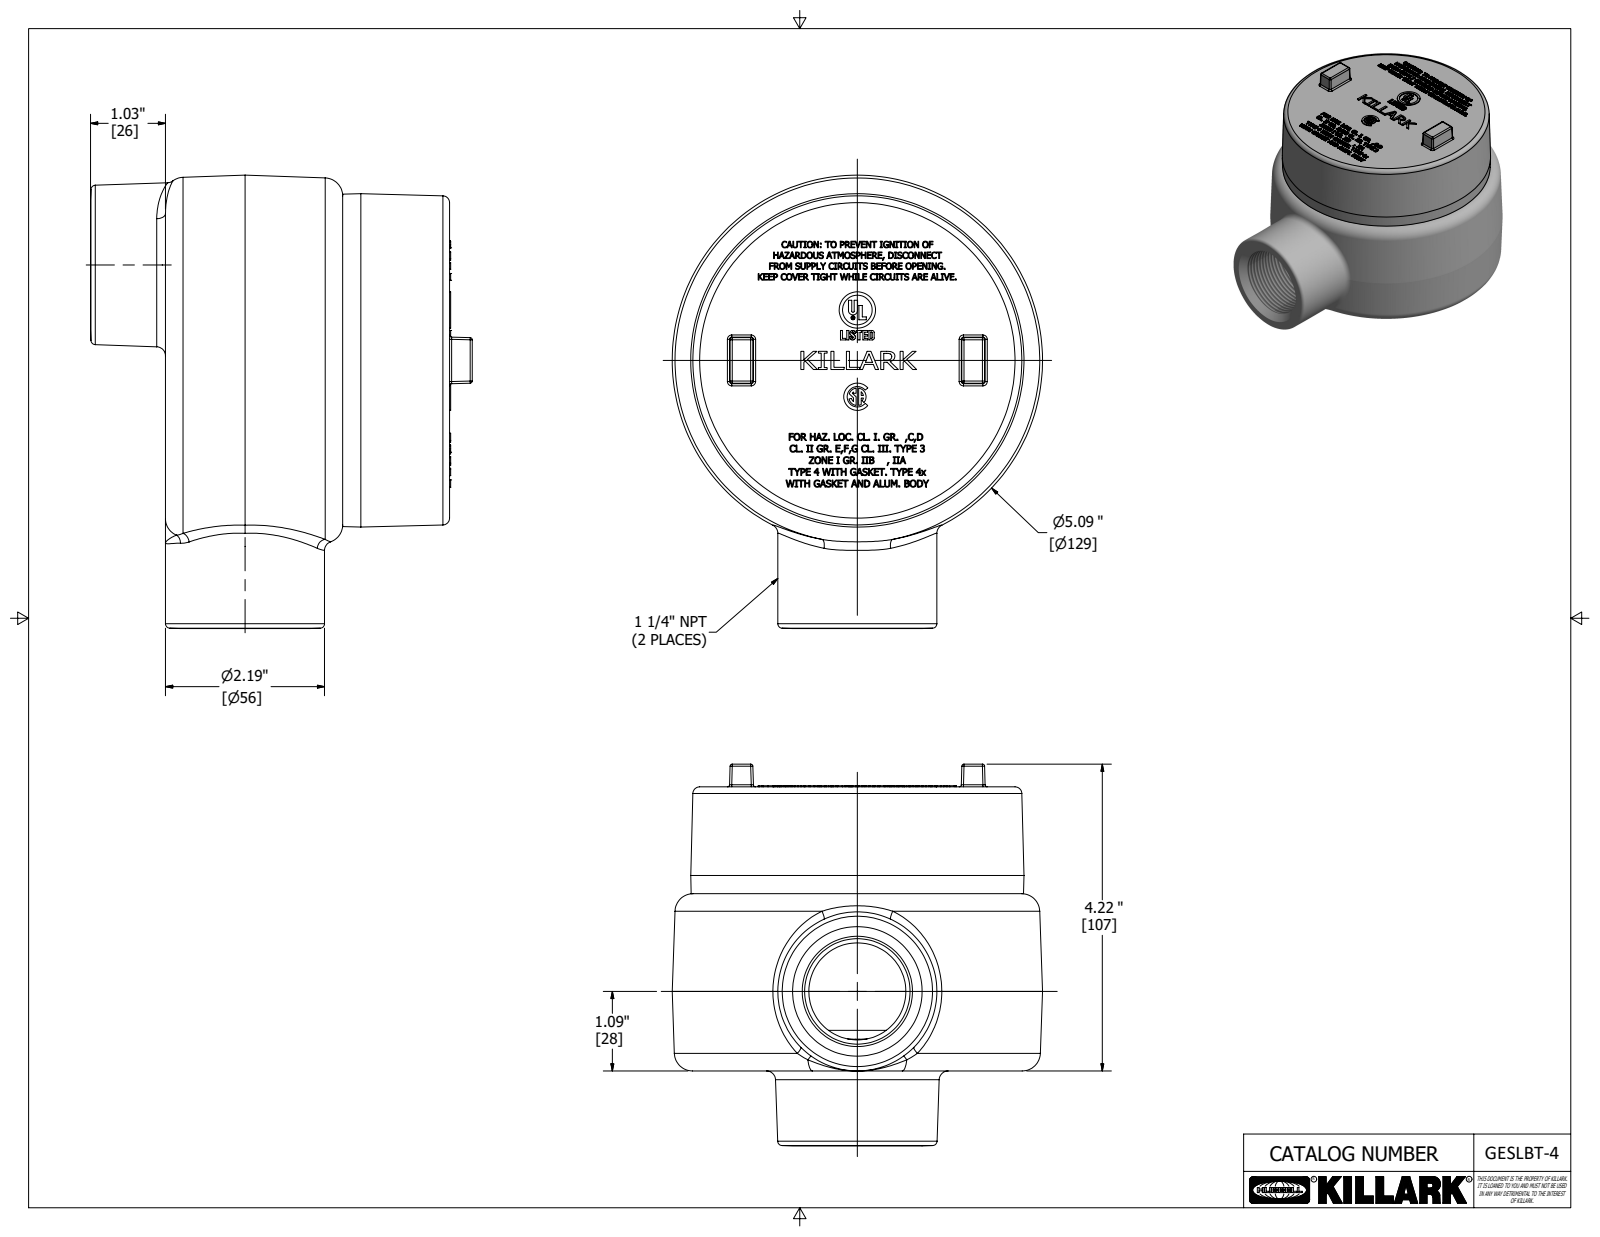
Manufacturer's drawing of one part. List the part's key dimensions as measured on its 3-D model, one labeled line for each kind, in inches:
Part name (STEP PRODUCT): GESLBT-4; 0072311M; 0072200M
STEP written by: Autodesk Inventor 2020 (AUTOMOTIVE_DESIGN)
Units: inches
Bodies: 2 solids, 4225 faces (2522 planar, 93 cylindrical, 1610 other)
Overall size (bounding box): 6.234 × 5.25 × 5.094
Volume: 35.26 in³ · Surface area: 223.4 in²
Round holes (diameter × count): ⌀1.334 ×2, ⌀0.047 ×1, ⌀0.196 ×1, ⌀0.407 ×1, ⌀3.86 ×1, ⌀4.057 ×1
Round bosses / shafts (diameter × count): ⌀4 ×1, ⌀3.867 ×1, ⌀2.187 ×1, ⌀0.5 ×1, ⌀0.056 ×1
Partial cylindrical surfaces — rounded edges, fillets, slot ends (radius × count): R0.03 ×20, R0.062 ×10, R0.01 ×2, R0.011 ×2, R0.028 ×2, R0.005 ×1, R0.006 ×1, R0.007 ×1
Main face-to-face distances: 3.469, 0.437, 3.906, 3.469, 3.031, 0.438, 2.437, 2, 1.031, 1.469
Hole centre spacings: 0.122, 0.589, 0.62, 0.693, 0.729, 1.313, 1.406, 1.469
